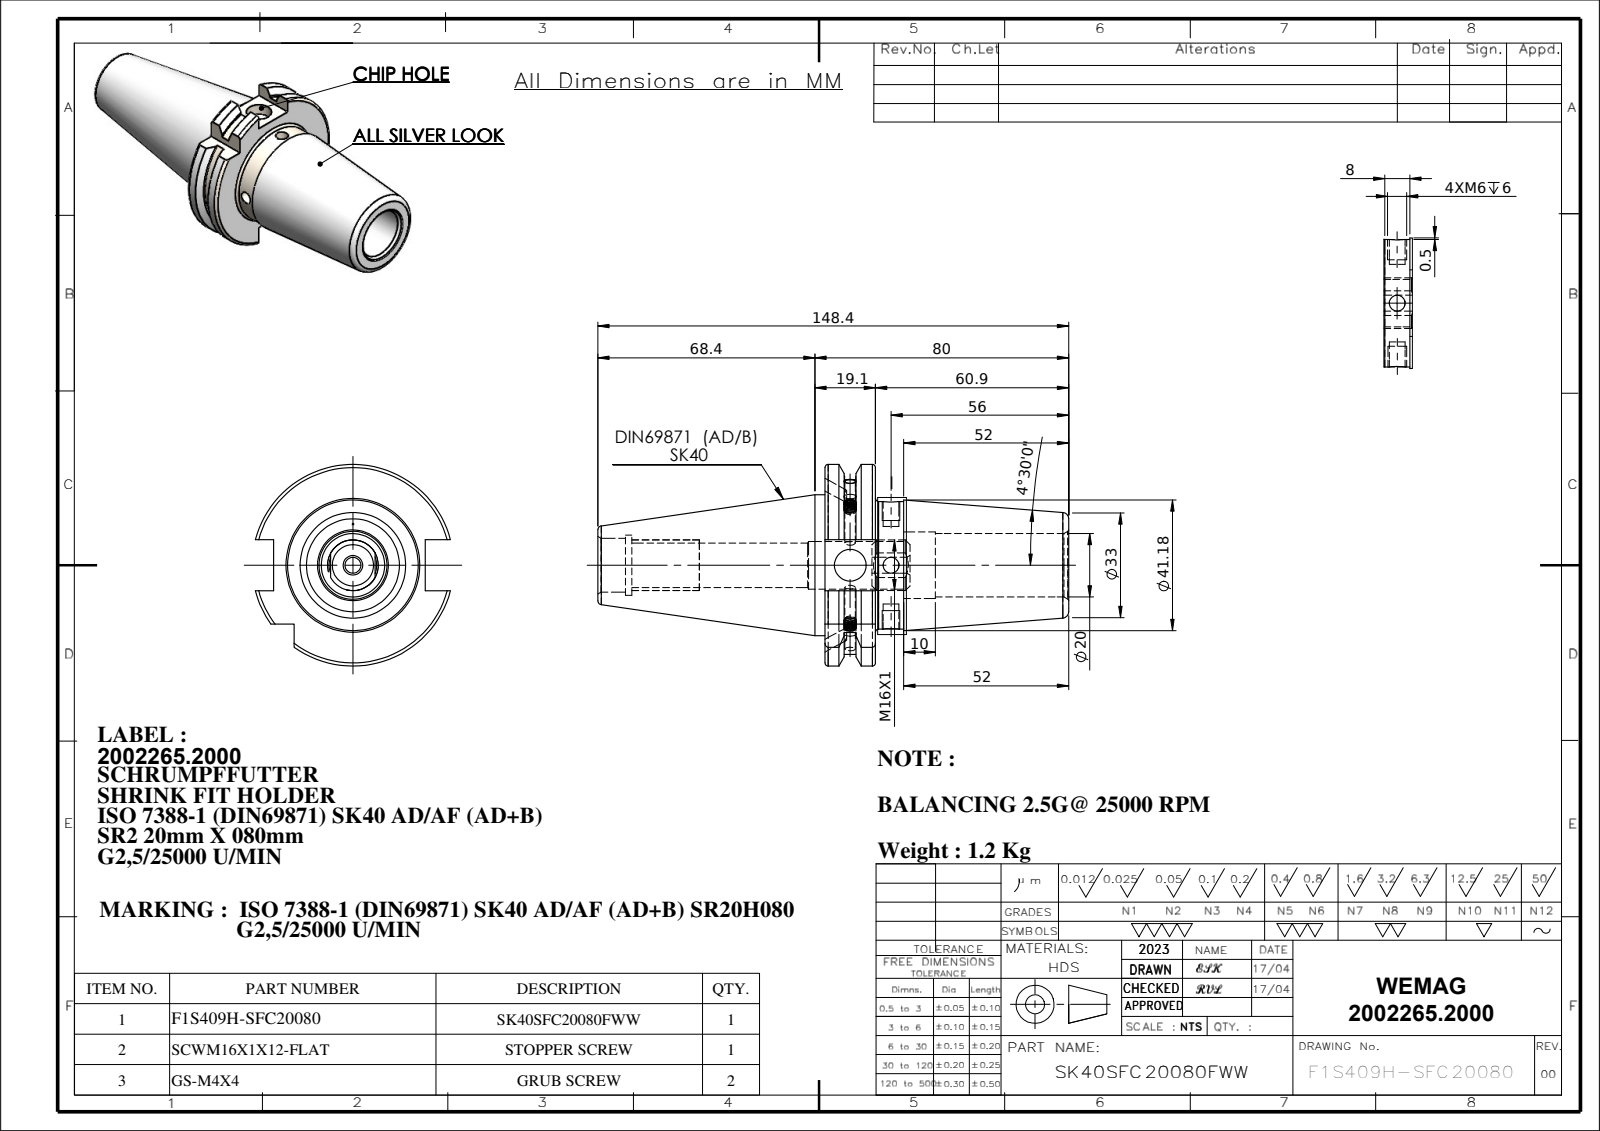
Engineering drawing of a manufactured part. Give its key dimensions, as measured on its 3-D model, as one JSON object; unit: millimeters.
{"part_name": "91406-SR220080; SK40SFC20080FWW; GS-M4X4_DIN 913 - M4 x 4-N; SCWM16X1X12-FLAT", "step_written_by": "SolidWorks 2018 (CONFIG_CONTROL_DESIGN)", "units": "millimeters", "bodies": {"solids": 4, "faces": 224, "planar": 57, "cylindrical": 67, "other": 100}, "overall_size": [148.4, 63.55, 61.48], "volume_mm3": 148654, "surface_area_mm2": 33495, "round_holes": [[5, 3], [3.3, 1], [10, 1], [14, 1], [15, 1], [17, 1], [19, 1], [19.99, 1], [20.99, 1]], "round_bosses_or_shafts": [[4, 2], [44.45, 1], [40.18, 1]], "partial_cylinders_radius": [[8, 1], [28.12, 1], [31.77, 1]], "face_to_face_distances": [15.9, 60.9, 76.8, 24.8, 8.9, 52, 16.1, 47.8, 2, 87.7], "hole_center_spacings": [12.85]}
